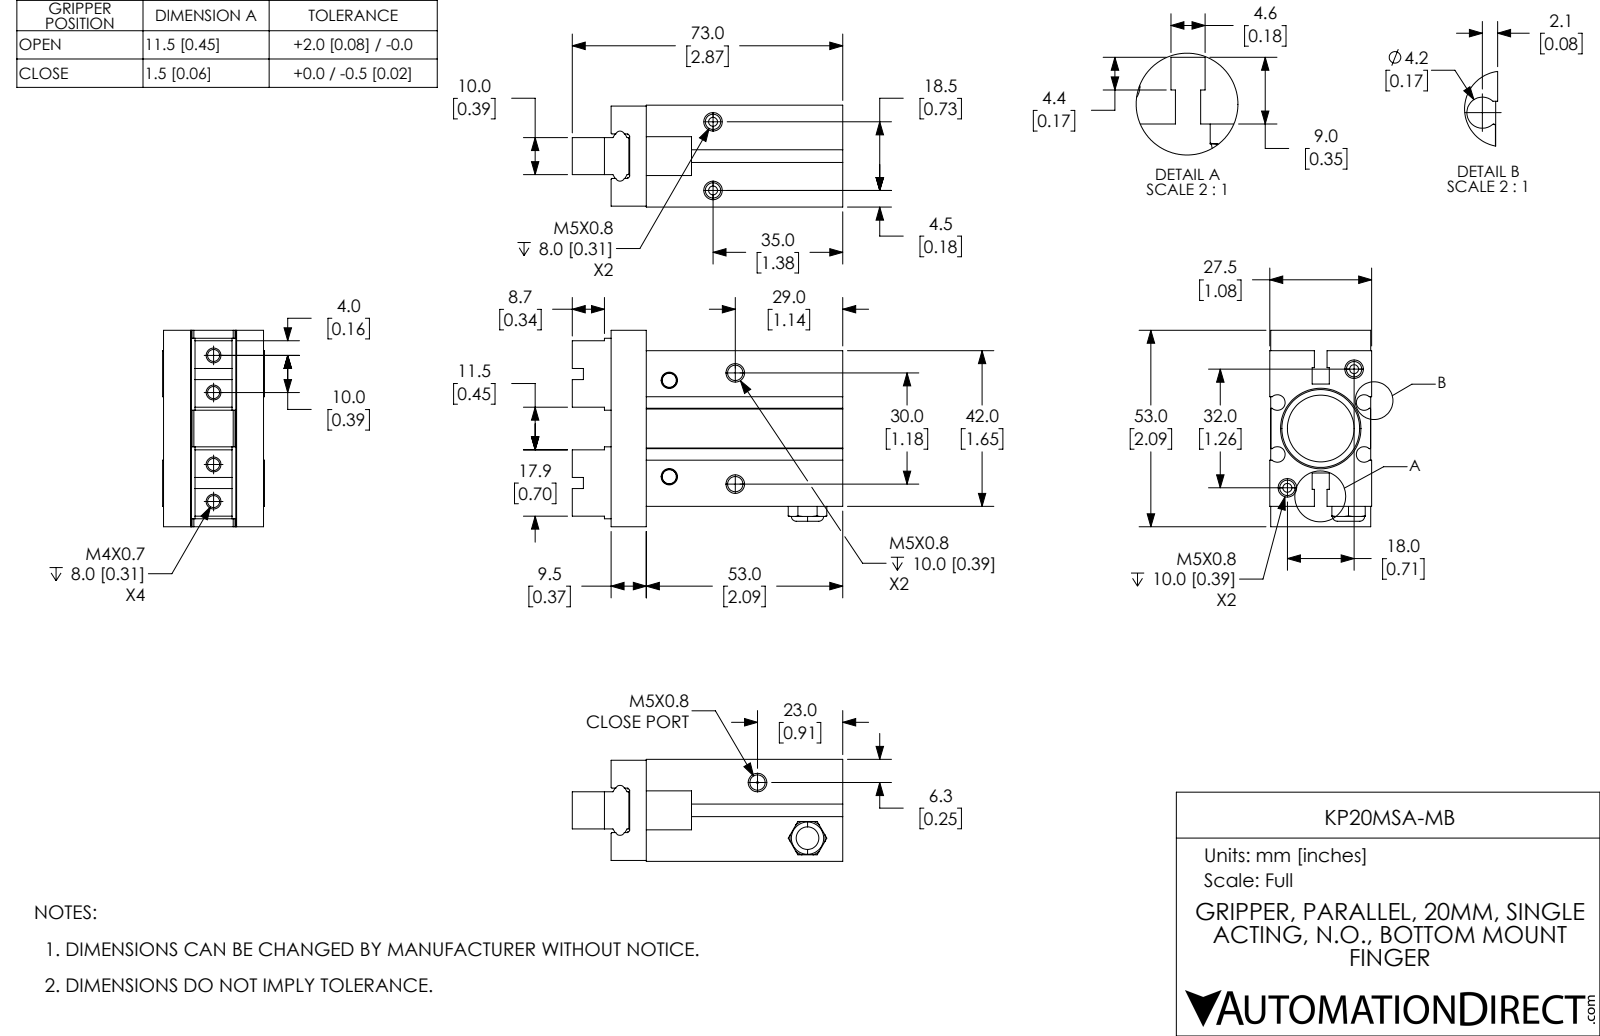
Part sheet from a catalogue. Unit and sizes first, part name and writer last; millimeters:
Units: millimetres
Overall size (bounding box): 73 × 53 × 27.5
Round holes (diameter × count): ⌀4.13 ×8, ⌀3.24 ×4, ⌀0.5 ×2, ⌀5.02 ×2, ⌀6.1 ×1, ⌀18 ×1, ⌀21 ×1
Partial cylindrical surfaces — rounded edges, fillets, slot ends (radius × count): R0.2 ×8, R1.25 ×4, R2.1 ×4, R0.5 ×2
Main face-to-face distances: 8.5, 18.75, 27.5, 18.7, 42, 27.2, 8.25, 19, 8.2, 27.25
Hole centre spacings: 9.7, 9.73, 10, 10.99, 18.36, 19.7, 27.23, 29.4
Volume: 63 367 mm³ · Surface area: 21 735 mm²
Bodies: 3 solids, 265 faces (137 planar, 66 cylindrical, 62 other)
Part name (STEP PRODUCT): KP20MSA-MB; KP20MSA-MB-3; KP20MSA-MB-2; KP20MSA-MB-1
STEP written by: SolidWorks 2017 (CONFIG_CONTROL_DESIGN)
